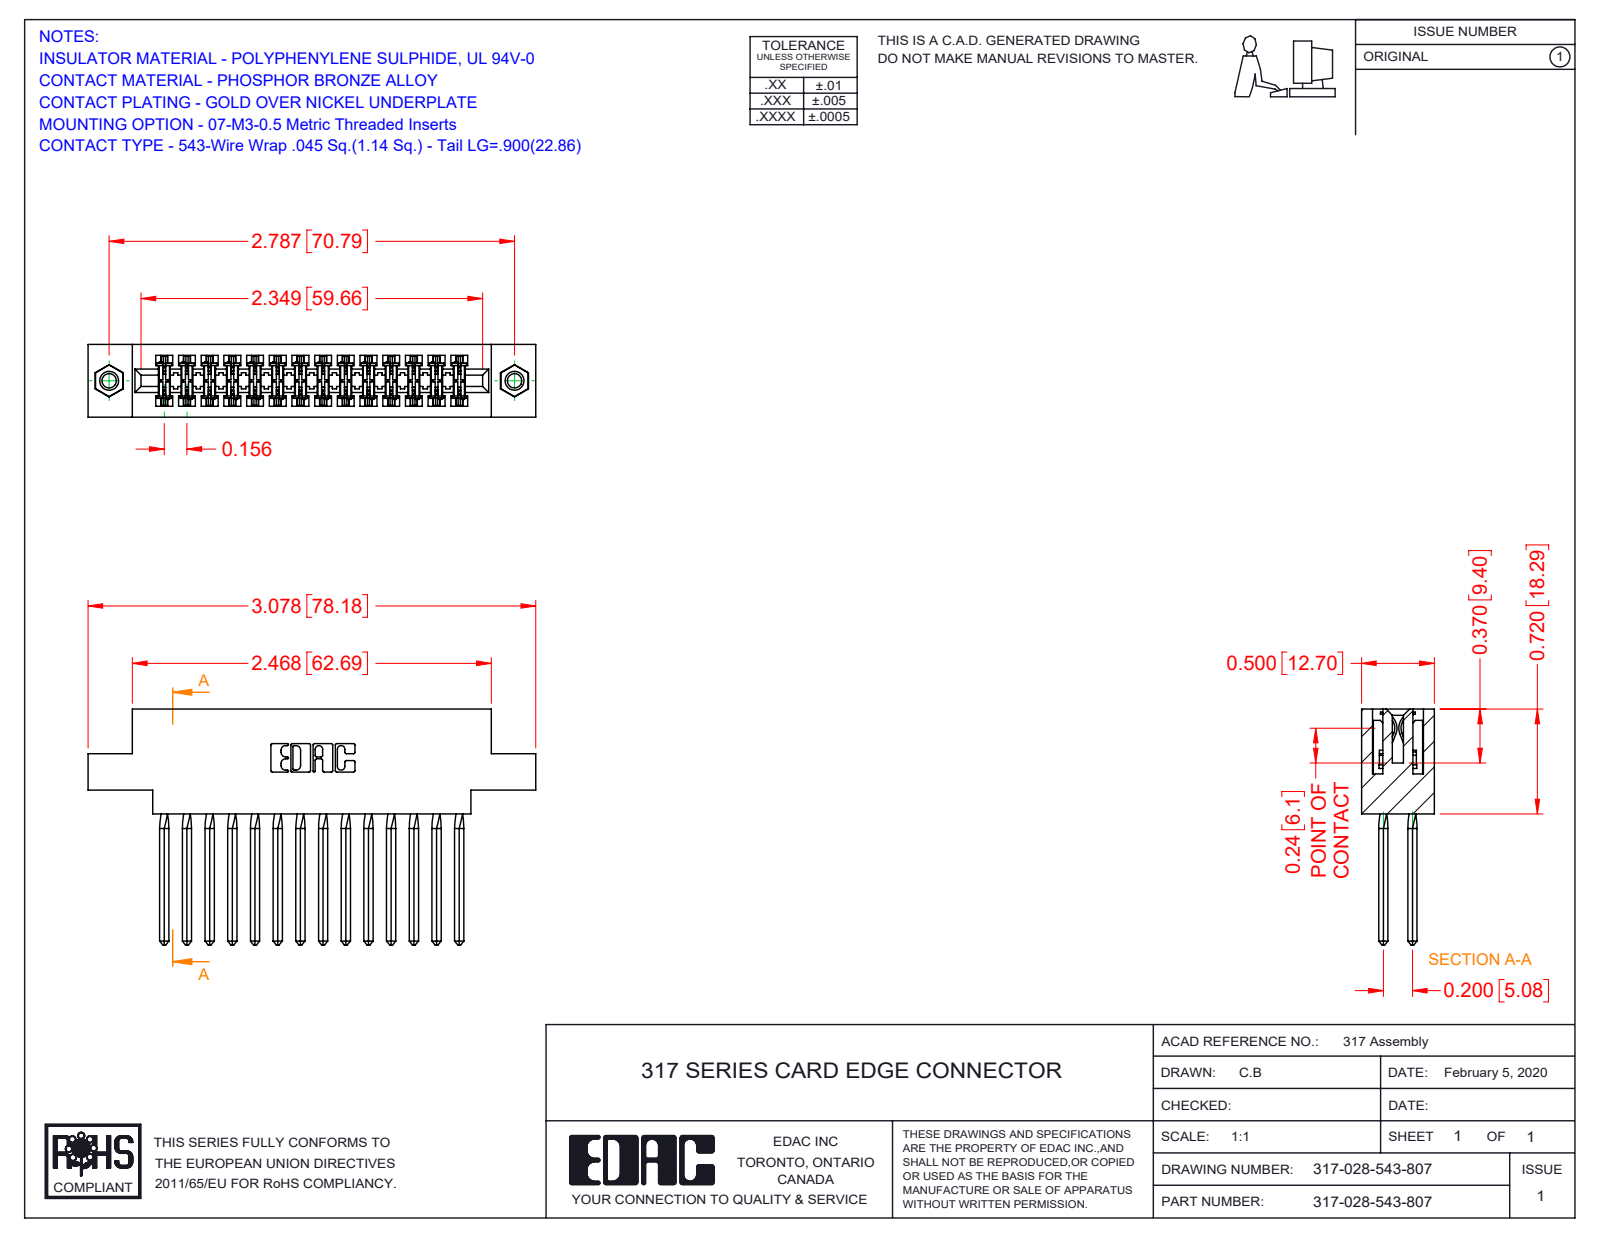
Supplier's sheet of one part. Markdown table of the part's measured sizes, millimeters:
| quantity | value |
| --- | --- |
| part name | 317 Part_.156 Dia - TI; 317-028-543-807; 317-290-001_543; 345-250-001_345-250-005-103 |
| STEP written by | SolidWorks 2016 (CONFIG_CONTROL_DESIGN) |
| units | millimeters |
| bodies | 31 solids, 2654 faces (2134 planar, 392 cylindrical, 128 other) |
| overall size | 78.2 × 41.1 × 12.7 |
| volume | 12 300 mm³ |
| surface area | 17 600 mm² |
| round holes (diameter × count) | 2.5 × 2, 3.2 × 2, 4 × 2 |
| round bosses / shafts (diameter × count) | 3.9 × 2 |
| partial cylindrical surfaces (radius × count) | 0.4 × 56, 0.3 × 22, 0.2 × 6, 0.8 × 6, 0.7 × 3, 2.4 × 2, 2.5 × 2, 2.8 × 2 |
| main face-to-face distances | 12.7, 1.9, 10.8, 2.8, 5.6, 8.9, 8.4, 3.5, 2.9, 18.3 |
| hole center spacings | 70.8 |
